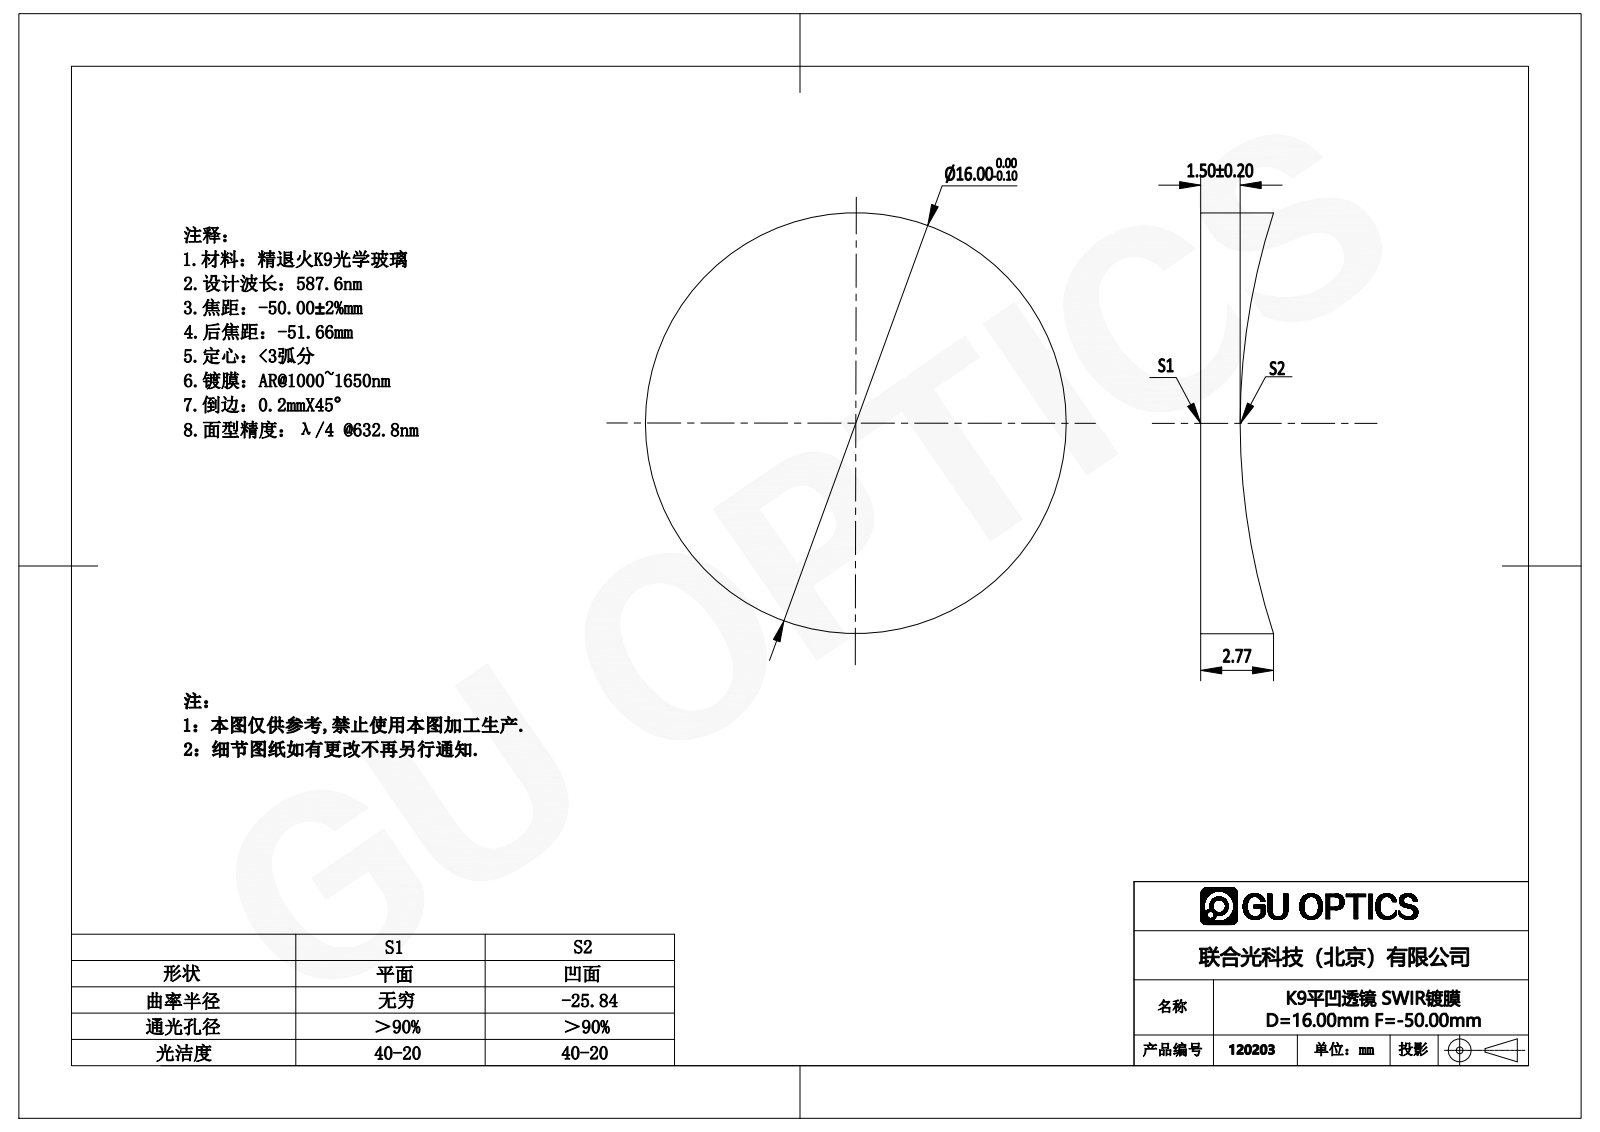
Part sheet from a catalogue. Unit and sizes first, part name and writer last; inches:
Units: inches
Overall size (bounding box): 0.63 × 0.63 × 0.109
Round bosses / shafts (diameter × count): ⌀0.63 ×1
Volume: 0.026 in³ · Surface area: 0.846 in²
Bodies: 1 solid, 5 faces (1 planar, 2 cylindrical, 2 other)
Part name (STEP PRODUCT): 120143
STEP written by: SolidWorks 2016 (AUTOMOTIVE_DESIGN)
